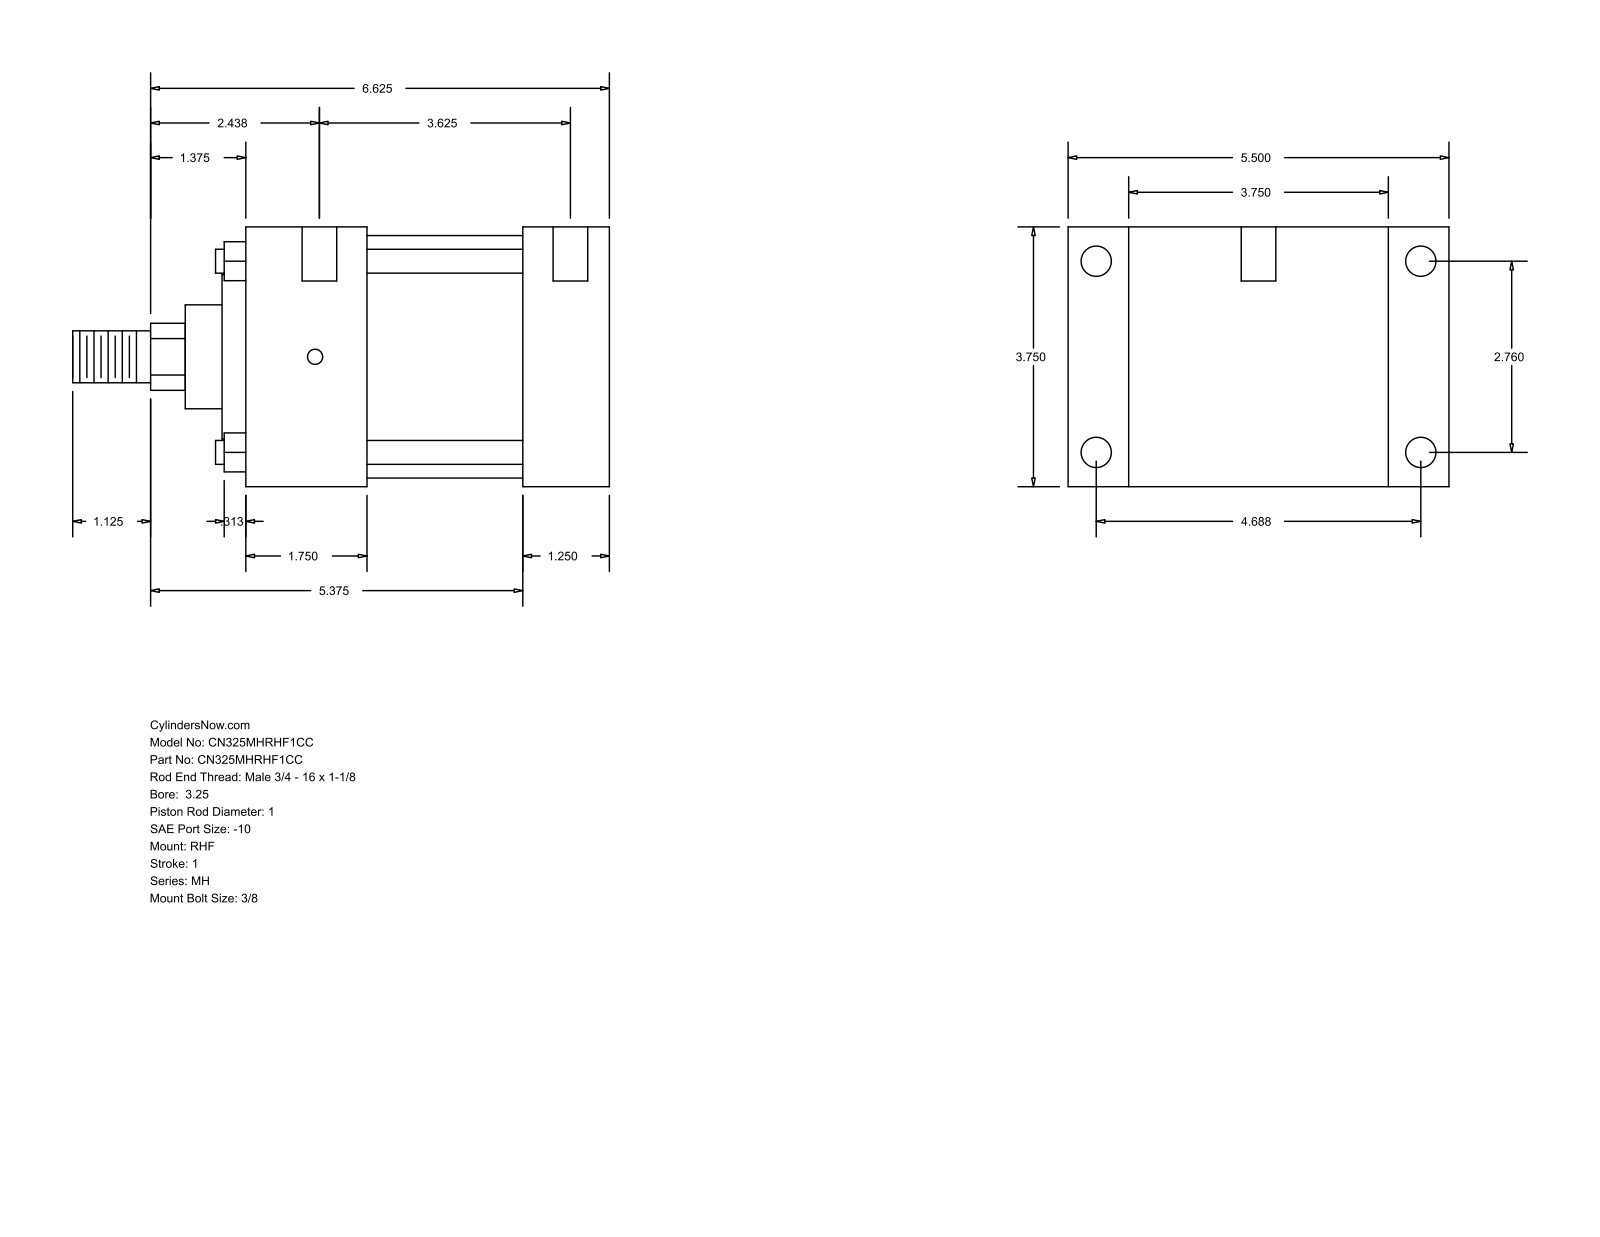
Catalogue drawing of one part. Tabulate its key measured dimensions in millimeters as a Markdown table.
| quantity | value |
| --- | --- |
| part name | MH_RHF__0325_1 |
| STEP written by | GSSL Pune (CONFIG_CONTROL_DESIGN) |
| units | millimeters |
| bodies | 0 solids, 90 faces (61 planar, 29 cylindrical, 0 other) |
| overall size | 196.85 × 139.7 × 95.25 |
| round holes (diameter × count) | 5.56 × 4, 11.13 × 4, 12.7 × 2 |
| round bosses / shafts (diameter × count) | 8.76 × 4, 88.9 × 1, 60.33 × 1, 38.1 × 1, 25.4 × 1, 19.05 × 1 |
| partial cylindrical surfaces (radius × count) | 12.29 × 1 |
| main face-to-face distances | 95.24, 31.75, 22.23, 117.47, 101.61, 133.36, 139.7, 44.46, 57.15, 88.9 |
| hole center spacings | 70.1, 98.42, 119.06, 138.16, 1.58, 4.76, 92.08, 93.66 |
